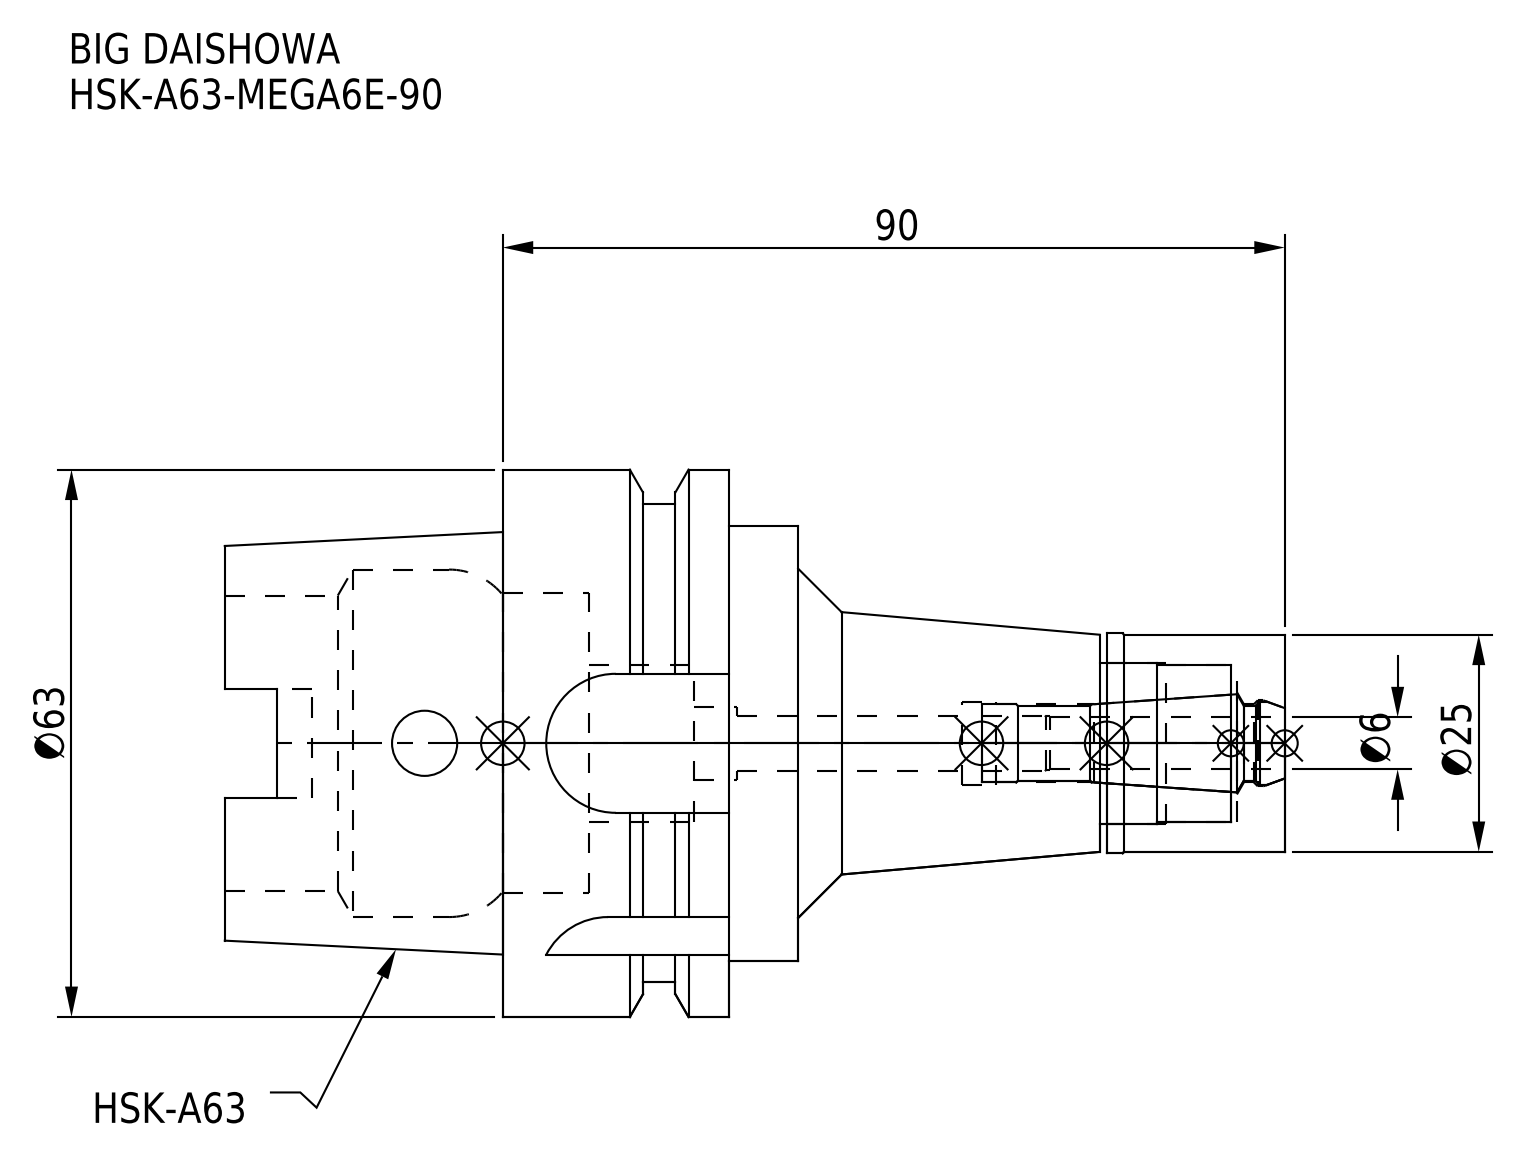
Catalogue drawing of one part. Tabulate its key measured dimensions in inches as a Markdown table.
| quantity | value |
| --- | --- |
| part name | MEN6_1.stp; HSK-A63-MEGA6E-90_1.stp; DXF_TEMP_ASSY_ASM_4_ASM.stp; HSK-A63-MEGA6E-90 (+3 more) |
| STEP written by | SolidWorks 2019 (CONFIG_CONTROL_DESIGN) |
| units | inches |
| bodies | 2 solids, 127 faces (45 planar, 54 cylindrical, 28 other) |
| overall size | 4.803 × 2.48 × 2.48 |
| volume | 7.729 in³ |
| surface area | 49.67 in² |
| round holes (diameter × count) | 0.252 × 1, 0.295 × 1, 0.331 × 1, 0.354 × 1, 0.378 × 1, 0.39 × 1, 0.709 × 1, 0.728 × 1, 1.339 × 1, 1.358 × 1, 1.575 × 1 |
| round bosses / shafts (diameter × count) | 2.48 × 1, 2.165 × 1, 1.969 × 1, 0.996 × 1, 0.984 × 1 |
| partial cylindrical surfaces (radius × count) | 0.11 × 2, 0.113 × 2, 0.315 × 2, 0.354 × 1 |
| main face-to-face distances | 1.024, 0.315, 1.339, 0.947, 0.632, 0.392, 2.205, 2.52, 3.152, 3.543 |
